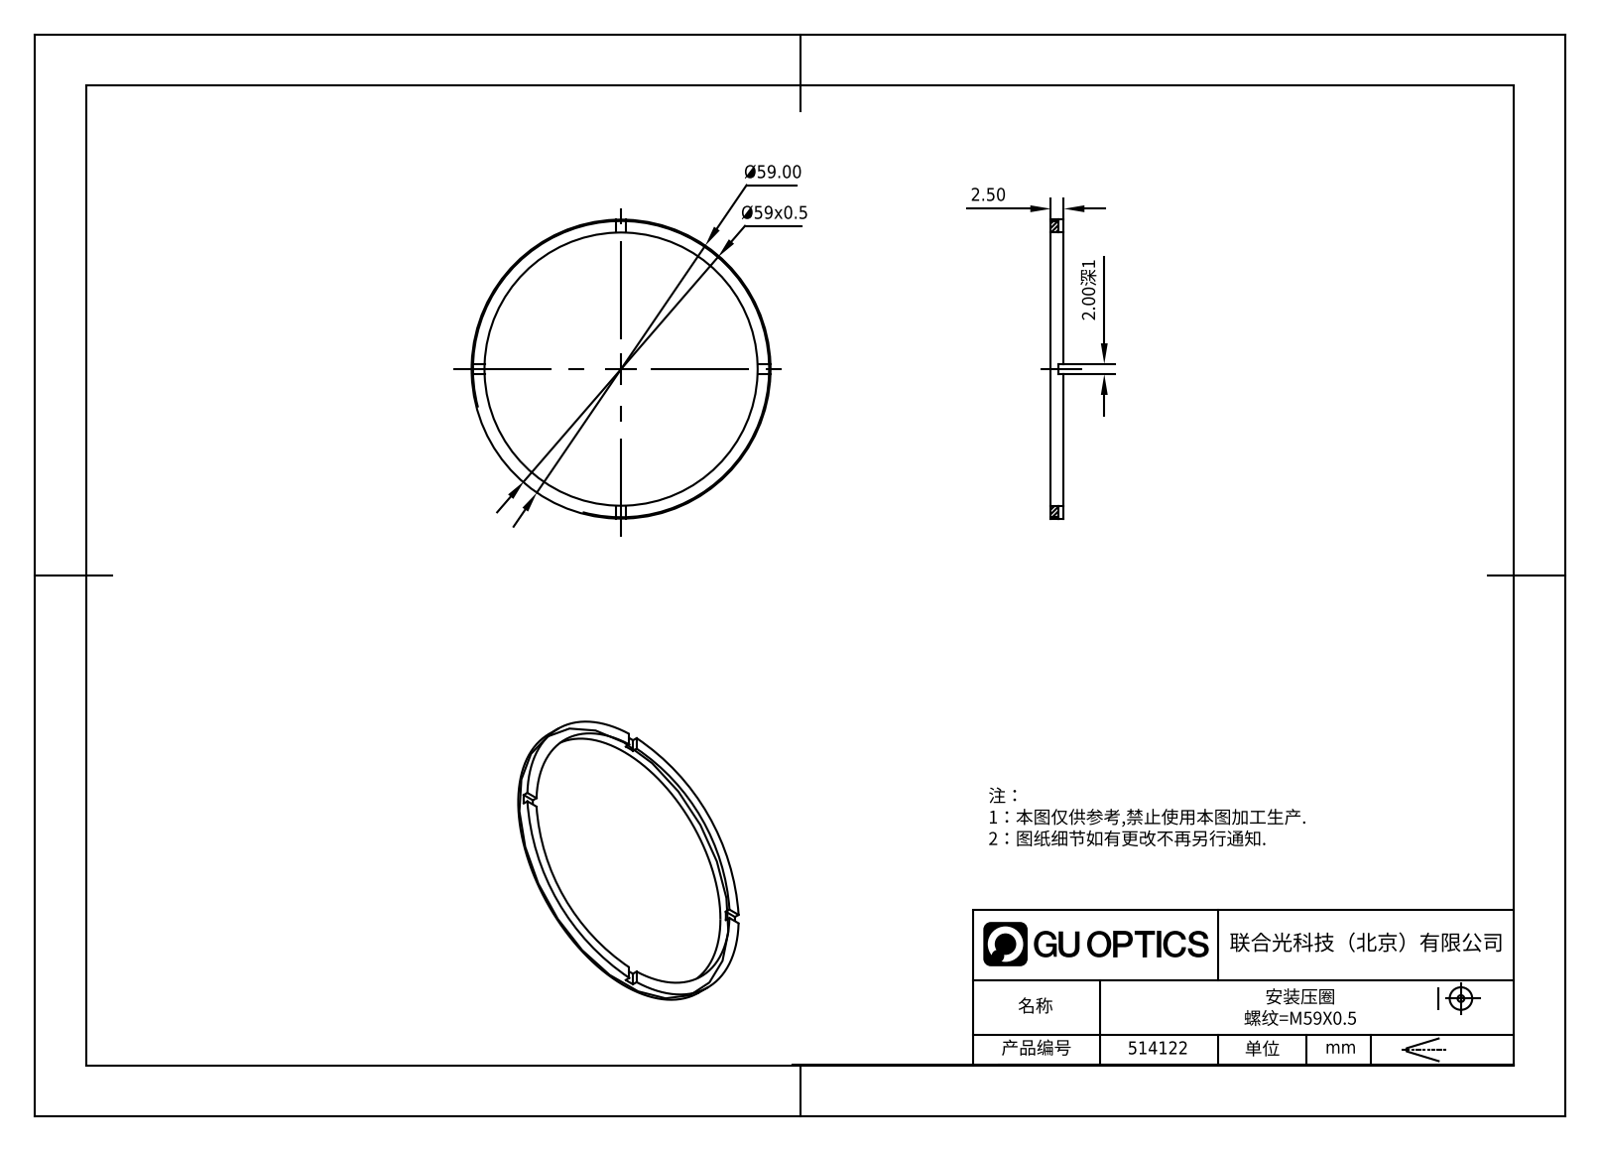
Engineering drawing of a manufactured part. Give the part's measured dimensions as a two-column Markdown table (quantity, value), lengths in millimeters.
| quantity | value |
| --- | --- |
| part name | 514122 |
| STEP written by | SolidWorks 2020 (CONFIG_CONTROL_DESIGN) |
| units | millimeters |
| bodies | 1 solid, 21 faces (17 planar, 4 cylindrical, 0 other) |
| overall size | 59 × 59 × 2.5 |
| volume | 1 089 mm³ |
| surface area | 1 779 mm² |
| round holes (diameter × count) | 54 × 1 |
| round bosses / shafts (diameter × count) | 59 × 1 |
| main face-to-face distances | 2.5, 1.5, 1, 2 |
